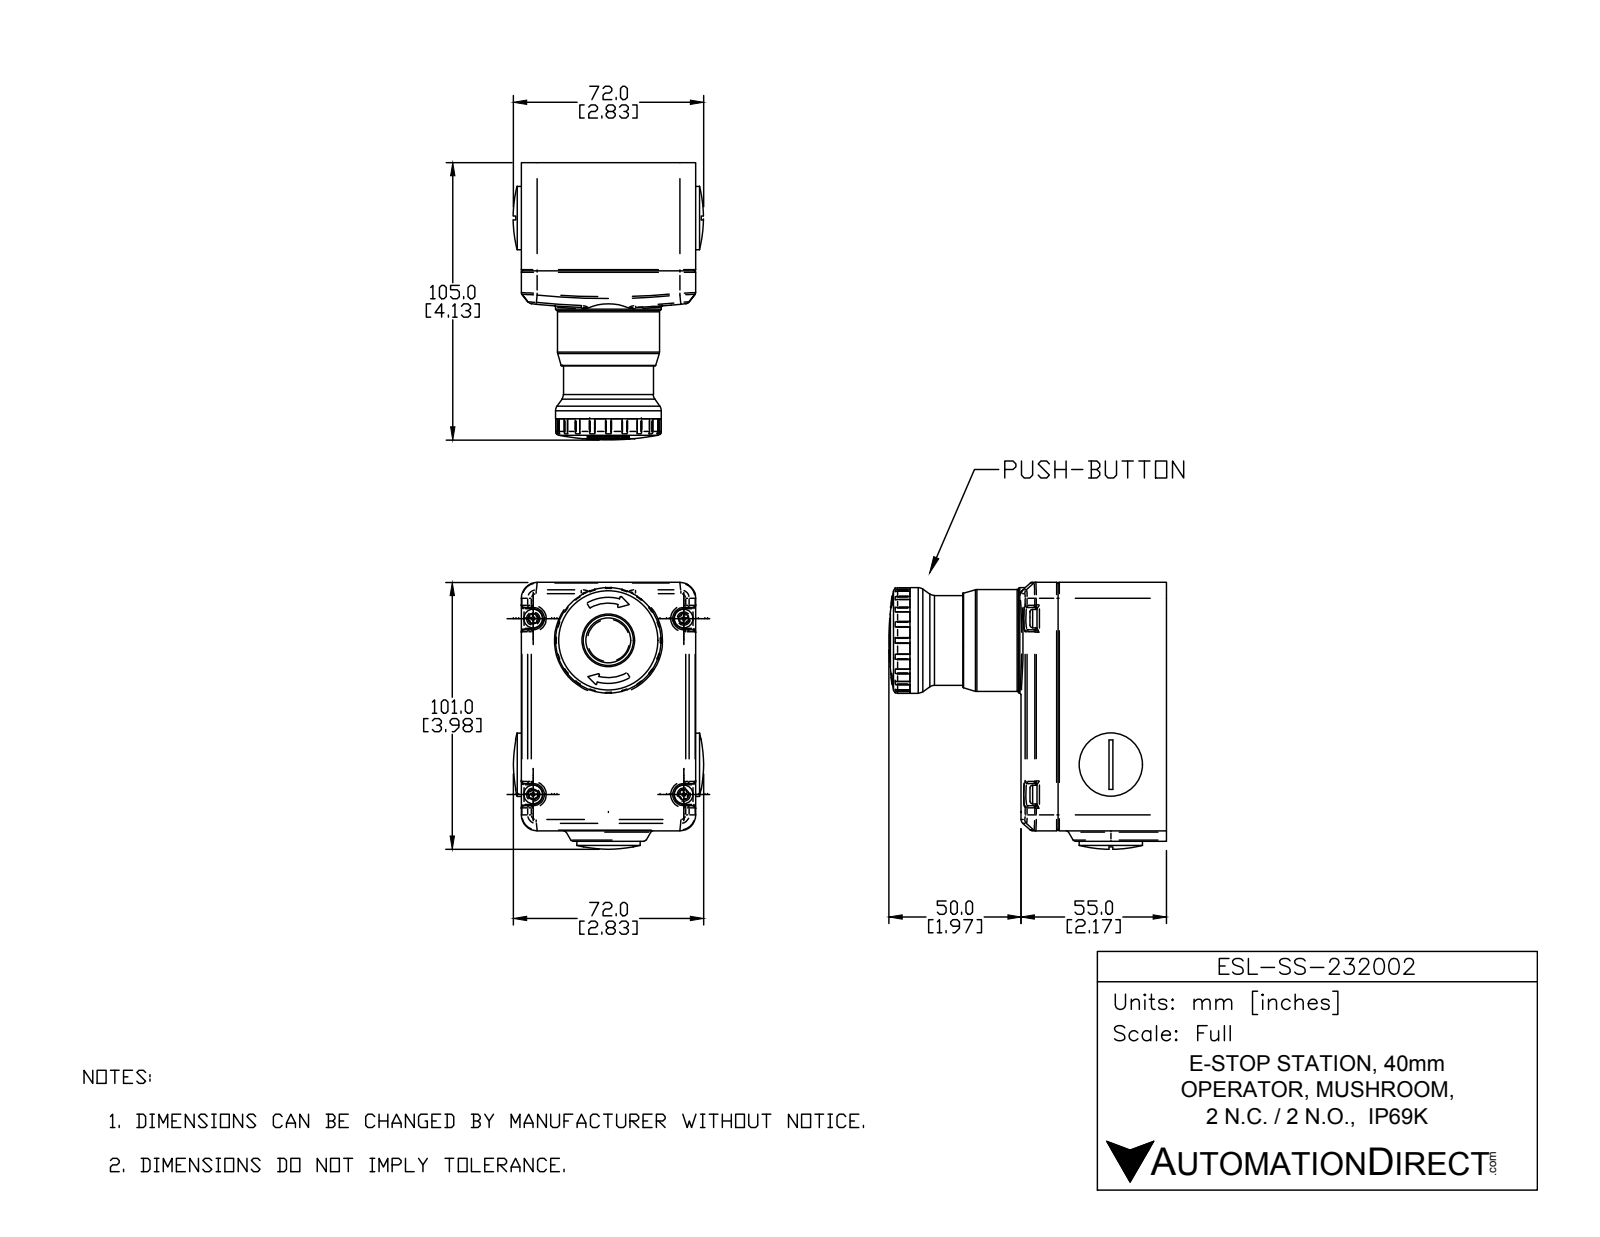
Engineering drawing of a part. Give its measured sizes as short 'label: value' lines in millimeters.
name: ESL-SS-232002
written by: SolidWorks 2016 (AUTOMOTIVE_DESIGN)
unit: mm
bodies: 11 solids, 674 faces (216 planar, 248 cylindrical, 210 other)
size: 105 × 100.99 × 71.98
volume: 363 454 mm³; area: 60 089 mm²
holes: 4× ⌀4.5, 1× ⌀31.1, 1× ⌀37
bosses: 4× ⌀7, 4× ⌀1, 2× ⌀24, 1× ⌀40, 1× ⌀38.6, 1× ⌀34
rounds: 80× R0.1, 24× R0.76, 14× R0.5, 4× R0.2, 4× R1, 4× R4.2, 4× R6, 2× R2
face distances: 41, 66, 56, 15, 98, 4, 94, 56.8, 15.8, 0.8
hole spacings: 31.38, 54, 71.31, 82, 98.18
